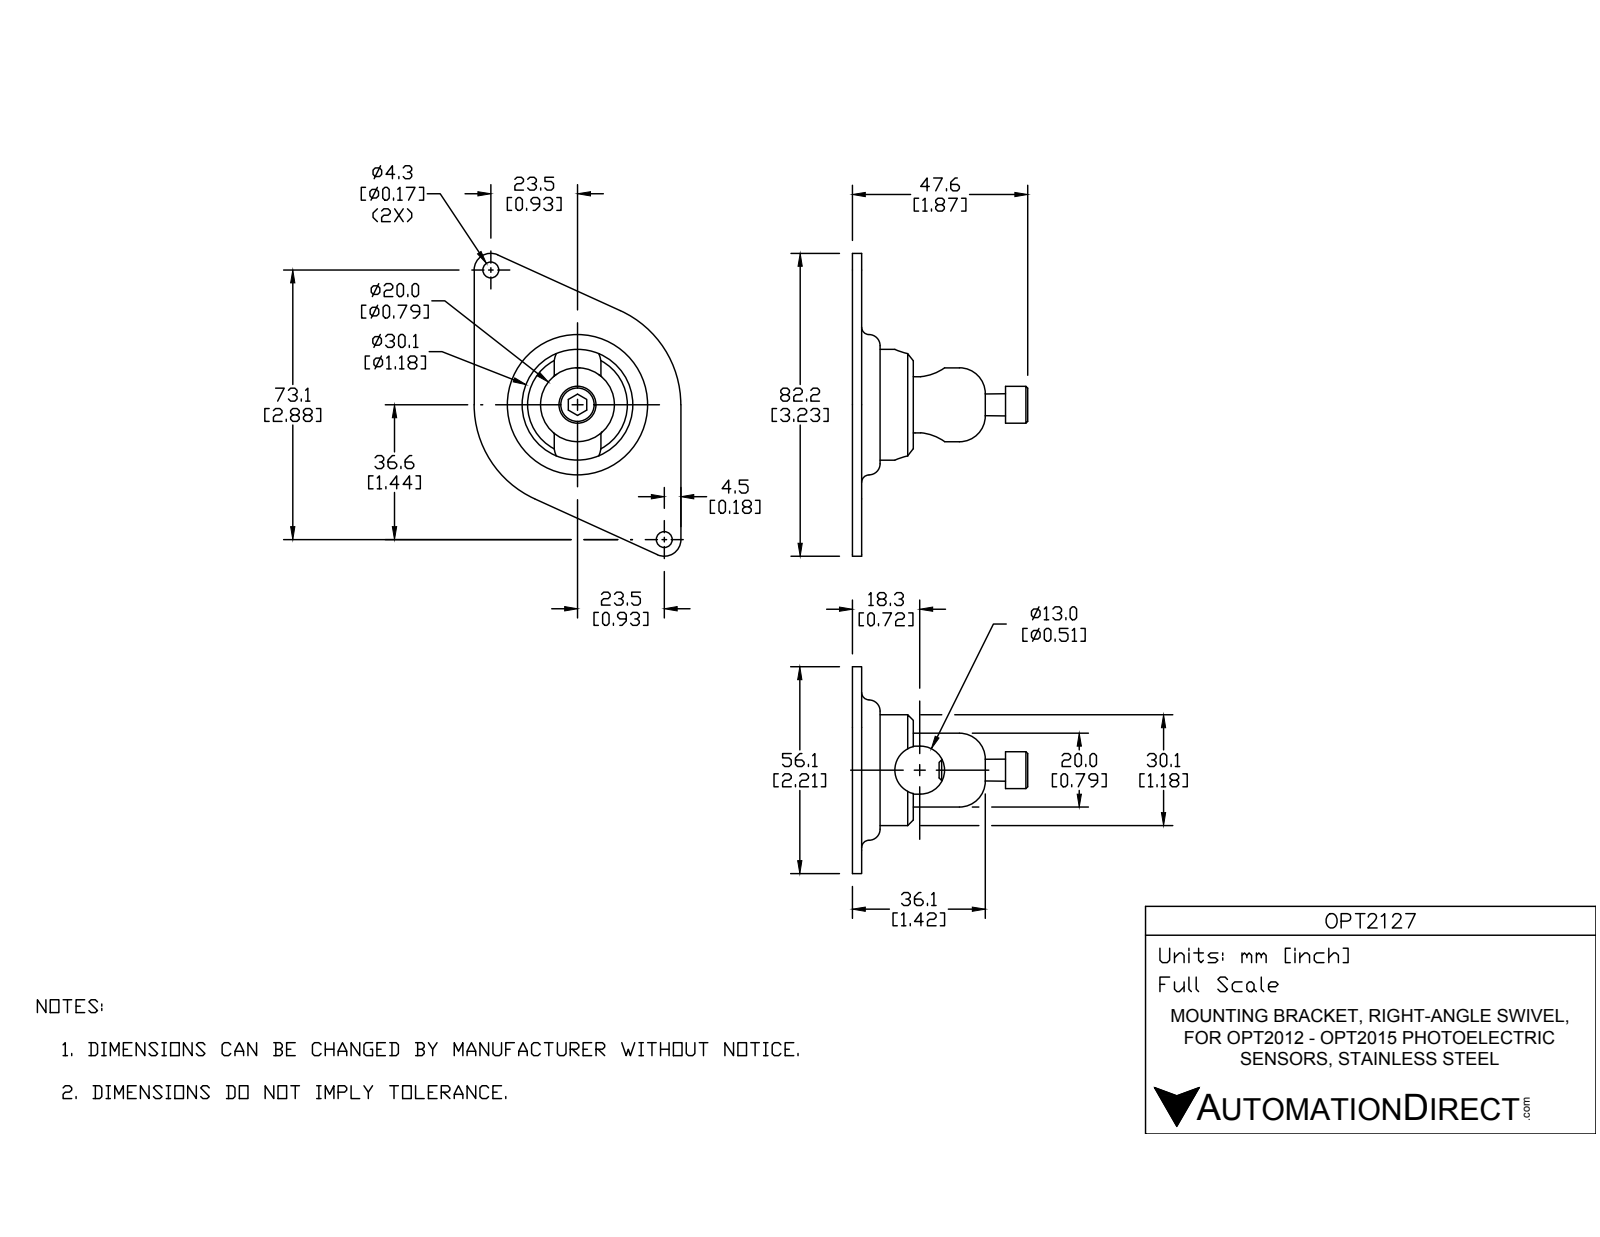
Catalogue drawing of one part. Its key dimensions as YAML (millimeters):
part_name: "1012426_BEFESTIGUNGSPLATTE_WTA; WS12AL"
step_written_by: "Solid Edge (automotive_design)"
units: millimeters
bodies: {solids: 4, faces: 122, planar: 56, cylindrical: 40, other: 26}
overall_size: [87.5, 82, 56]
volume: 41653
surface_area: 26378
round_holes:
  - {diameter: 4.3, count: 4}
  - {diameter: 20.1, count: 2}
  - {diameter: 20, count: 1}
  - {diameter: 21, count: 1}
round_bosses_or_shafts:
  - {diameter: 30, count: 1}
  - {diameter: 10, count: 1}
partial_cylinders:
  - {radius: 4.5, count: 4}
  - {radius: 6.5, count: 3}
  - {radius: 28, count: 2}
face_to_face_distances: [2.5, 5, 7.5, 1, 1.5, 6.5, 4, 9, 11.5, 16.5]
hole_center_spacings: [43.41, 86.82]
